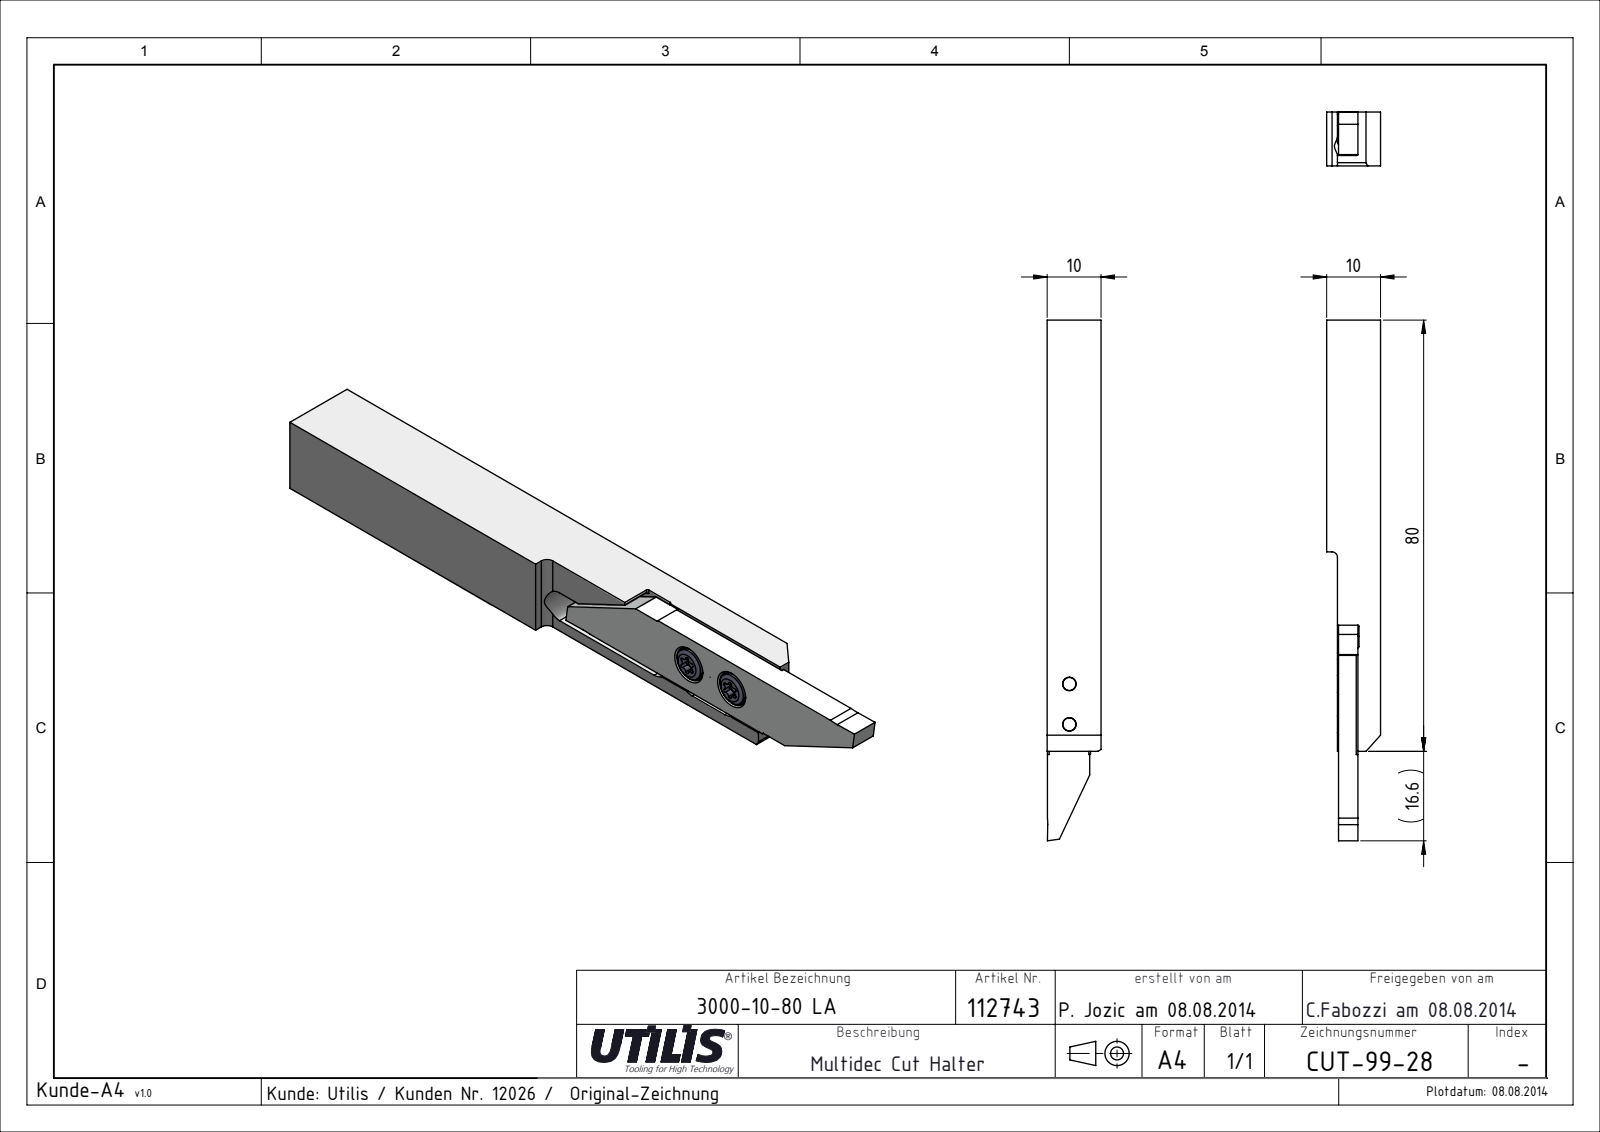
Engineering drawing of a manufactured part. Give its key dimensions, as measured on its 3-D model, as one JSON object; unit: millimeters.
{"part_name": "CUT-99-28", "step_written_by": "SolidWorks 2016 (AUTOMOTIVE_DESIGN)", "units": "millimeters", "bodies": {"solids": 1, "faces": 46, "planar": 34, "cylindrical": 8, "other": 4}, "overall_size": [96.6, 10, 10], "volume_mm3": 7410, "surface_area_mm2": 3819, "partial_cylinders_radius": [[2.1, 4], [10, 2], [1, 1]], "face_to_face_distances": [10, 2.2, 7.8, 8, 4.2, 3.8, 5.8, 3.6, 9.95, 2]}
